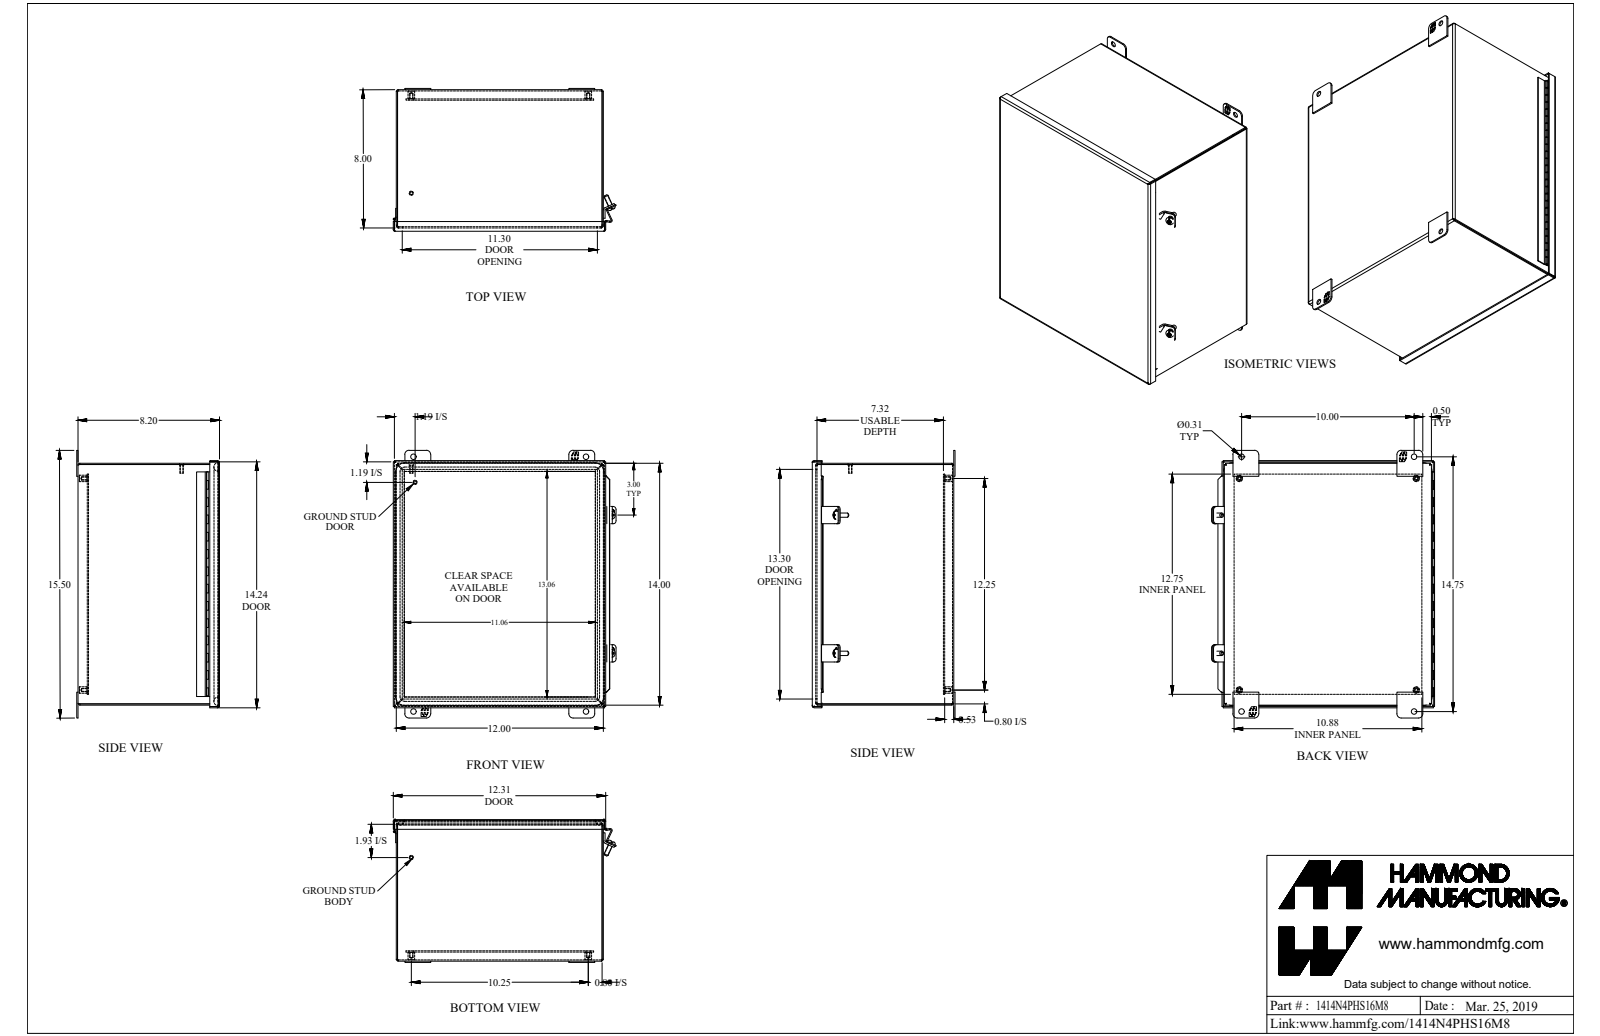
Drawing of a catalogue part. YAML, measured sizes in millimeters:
part_name: "1414N4PHS16M8"
step_written_by: "SolidWorks 2018 (AUTOMOTIVE_DESIGN)"
units: millimeters
bodies: {solids: 22, faces: 812, planar: 522, cylindrical: 218, other: 72}
overall_size: [393.7, 328, 210]
volume: 1449000
surface_area: 1598000
round_holes:
  - {diameter: 4, count: 4}
  - {diameter: 6.7, count: 4}
  - {diameter: 8, count: 4}
  - {diameter: 5.4, count: 2}
  - {diameter: 1.3, count: 1}
round_bosses_or_shafts:
  - {diameter: 9.5, count: 4}
  - {diameter: 6.4, count: 4}
  - {diameter: 12.2, count: 2}
  - {diameter: 4.8, count: 2}
  - {diameter: 2.5, count: 1}
  - {diameter: 1.1, count: 1}
partial_cylinders:
  - {radius: 6.4, count: 24}
  - {radius: 0.9, count: 13}
  - {radius: 2.7, count: 13}
  - {radius: 4.8, count: 8}
  - {radius: 0.2, count: 4}
  - {radius: 1.2, count: 4}
  - {radius: 2, count: 4}
  - {radius: 3, count: 4}
face_to_face_distances: [1.8, 206.4, 192.9, 13.5, 303, 1.8, 353.8, 208.2, 206.4, 204.5]
hole_center_spacings: [259.1, 405.7, 31.9, 342.9, 428.6, 260.4, 260.4, 311.2]
